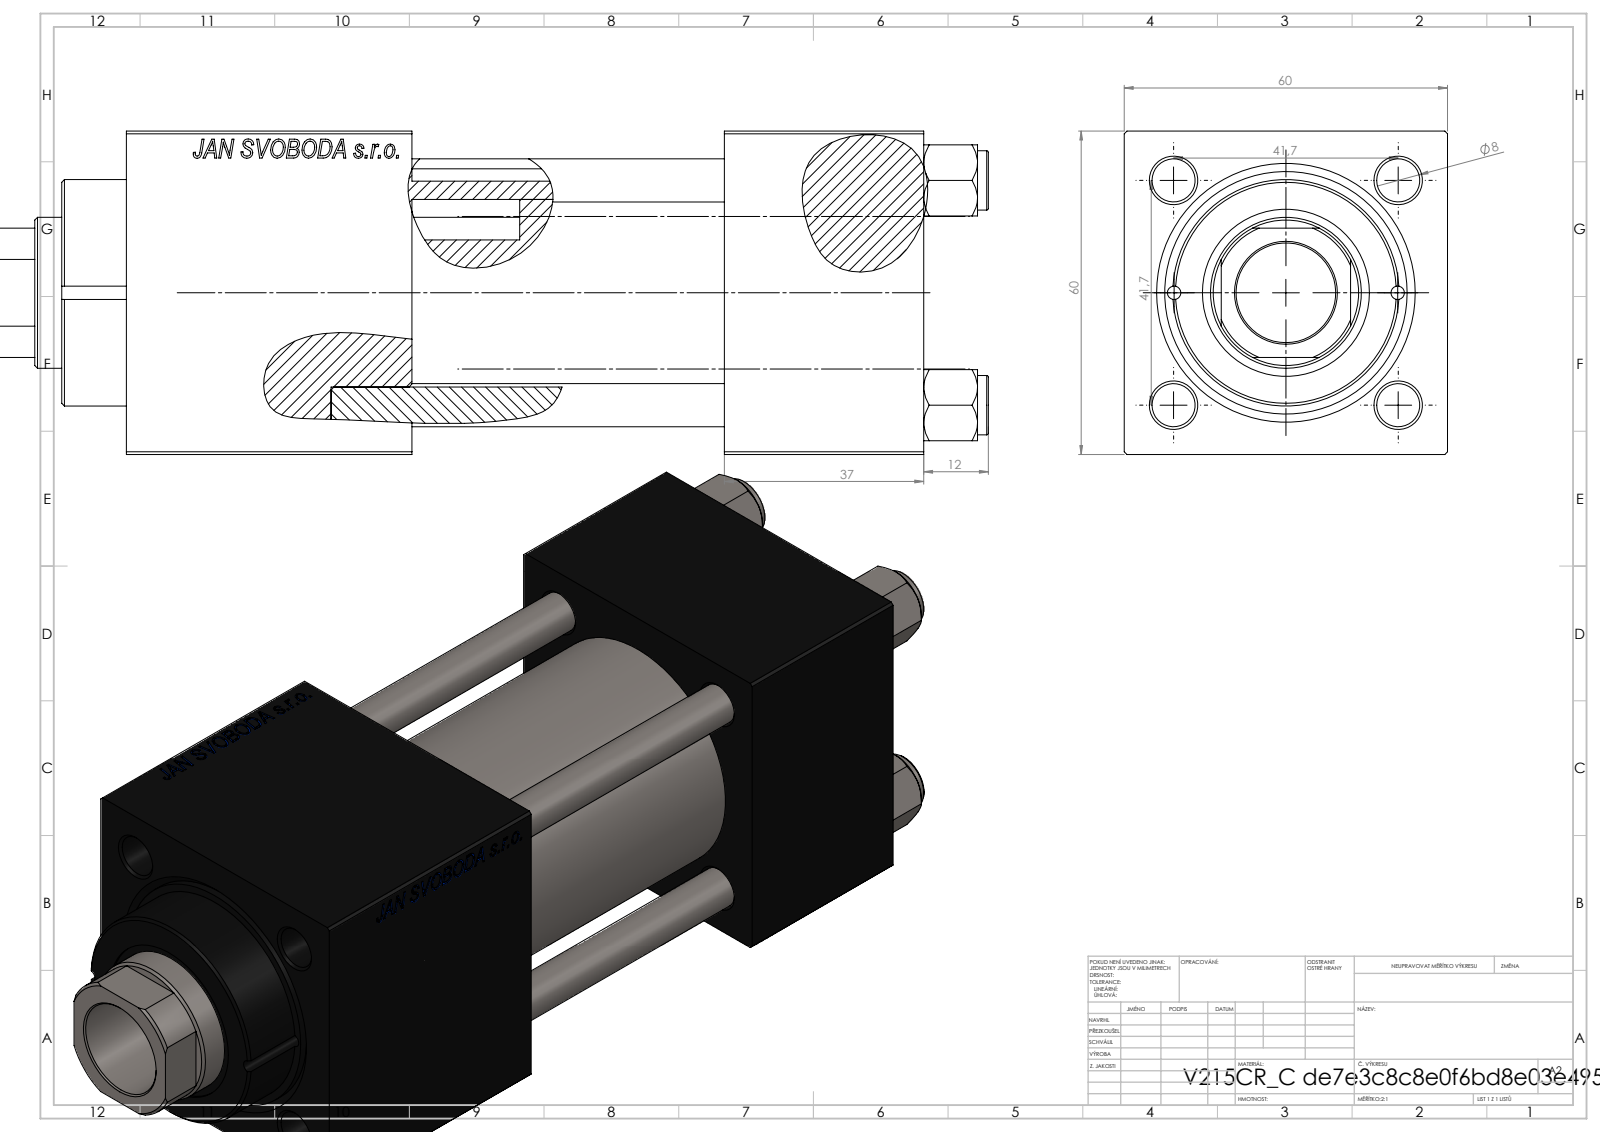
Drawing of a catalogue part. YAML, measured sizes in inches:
part_name: "NUT_M5_C; V215_VC_A; V215CR_C_Body; V215CR_C_TYCINKA (+1 more)"
step_written_by: "SolidWorks 2019 (CONFIG_CONTROL_DESIGN)"
units: inches
bodies: {solids: 11, faces: 1155, planar: 528, cylindrical: 91, other: 536}
overall_size: [7.283, 2.362, 2.362]
volume: 25.87
surface_area: 172.9
round_holes:
  - {diameter: 0.315, count: 4}
  - {diameter: 0.098, count: 2}
  - {diameter: 0.276, count: 2}
  - {diameter: 0.656, count: 2}
  - {diameter: 0.945, count: 2}
  - {diameter: 0.728, count: 1}
  - {diameter: 1.102, count: 1}
  - {diameter: 1.22, count: 1}
  - {diameter: 1.575, count: 1}
  - {diameter: 1.772, count: 1}
round_bosses_or_shafts:
  - {diameter: 0.433, count: 4}
  - {diameter: 1.811, count: 1}
  - {diameter: 1.654, count: 1}
partial_cylinders:
  - {radius: 0.531, count: 1}
face_to_face_distances: [2.362, 1.457, 2.283, 3.74, 2.087, 4.697, 3.24, 0.957, 5.827, 4.37]
hole_center_spacings: [0.821, 1.161, 1.642, 1.832, 0.817, 2.322, 1.634, 3.642]
